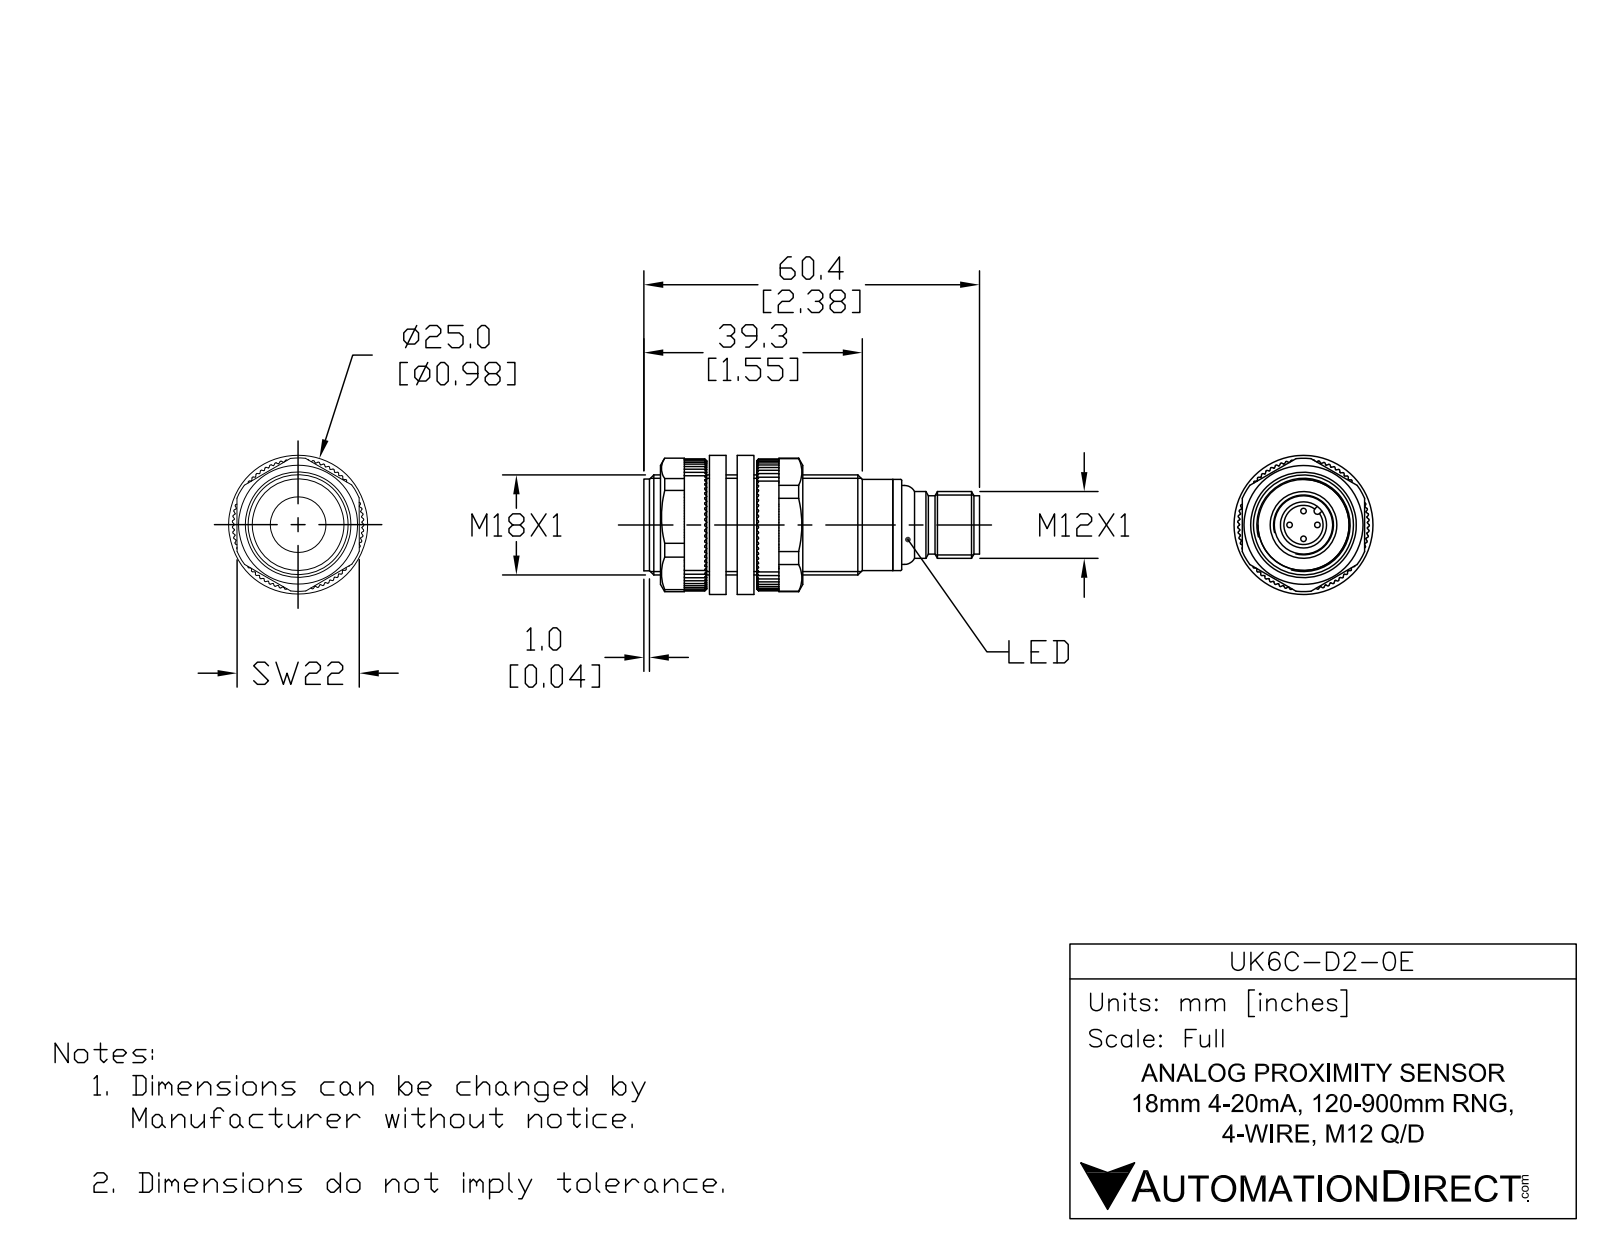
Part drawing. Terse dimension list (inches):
name: UK6C-D2-0E
written by: SolidWorks 2017 (AUTOMOTIVE_DESIGN)
unit: in
bodies: 4 solids, 86 faces (15 planar, 36 cylindrical, 35 other)
size: 2.374 × 0.709 × 0.709
volume: 0.759 in³; area: 7.648 in²
holes: 1× ⌀0.276, 1× ⌀0.327, 1× ⌀0.374
bosses: 4× ⌀0.039, 1× ⌀0.709, 1× ⌀0.646, 1× ⌀0.622, 1× ⌀0.559, 1× ⌀0.472, 1× ⌀0.413
rounds: 1× R0.024
face distances: 1.724, 0.039, 1.764, 0.039, 1.763, 1.823, 1.822, 1.783, 0.059, 2.024
